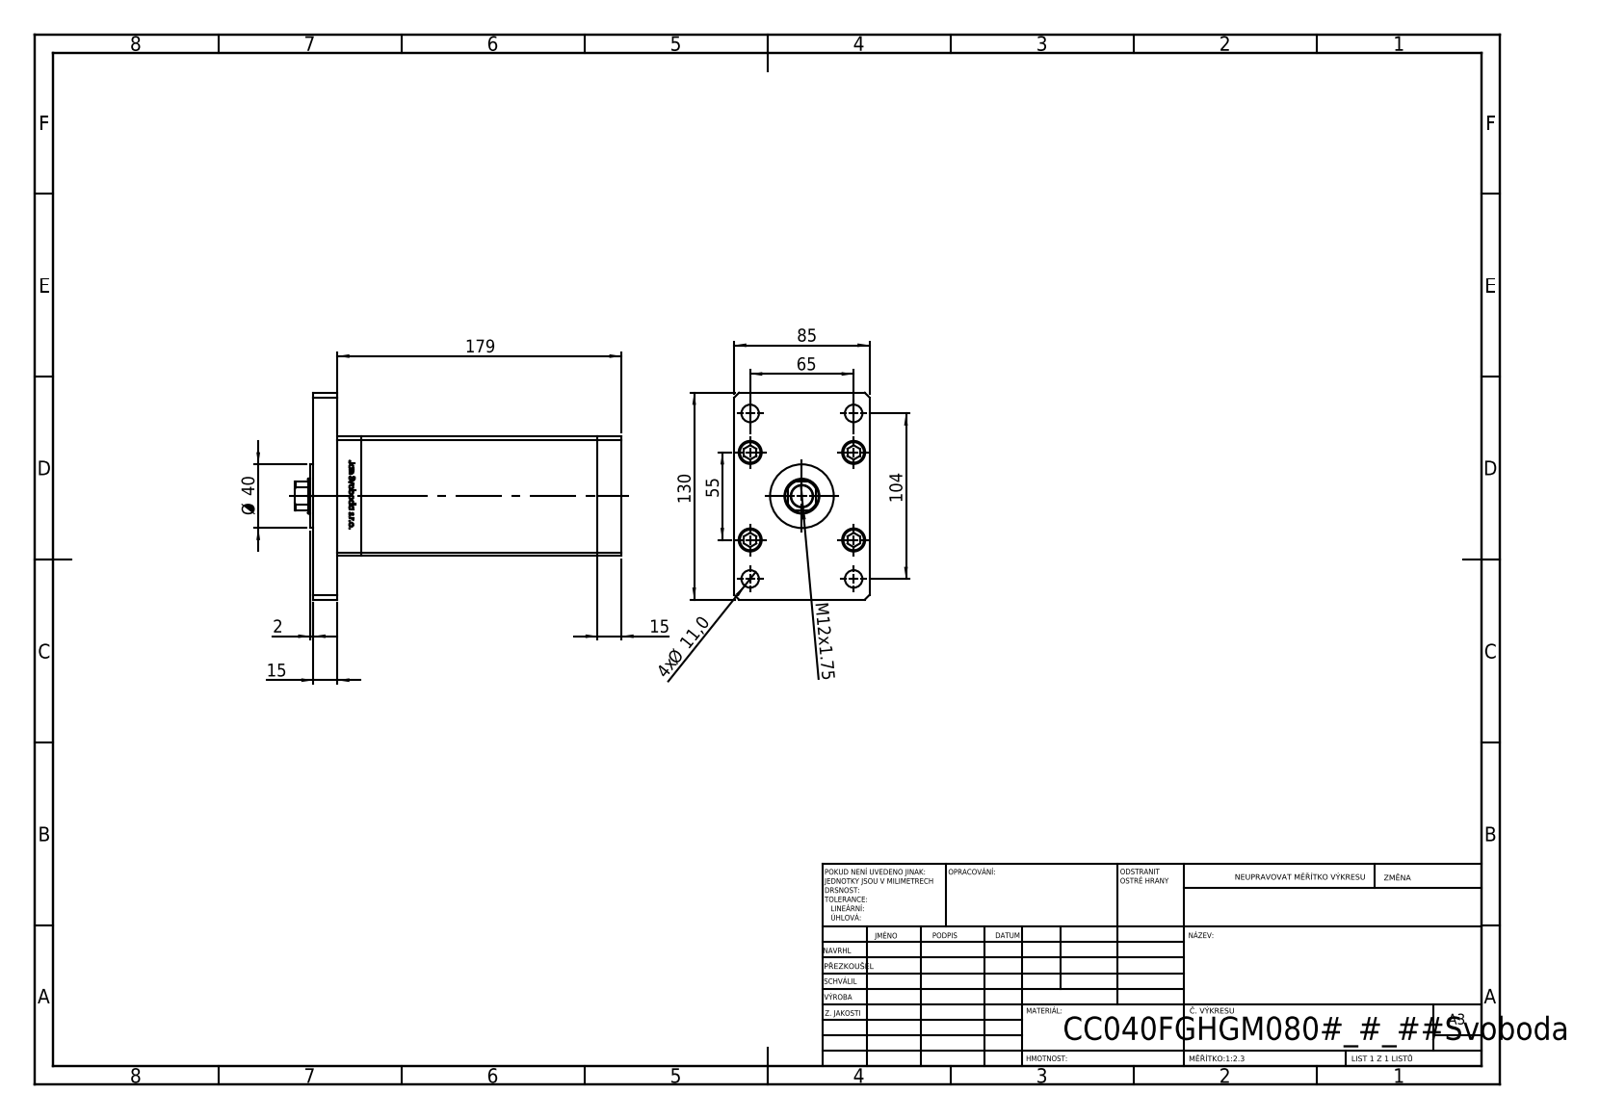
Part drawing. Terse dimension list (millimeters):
name: V220C_F_MIDDLE; V220C_F; V220C_FRONT_F; ALLEN BOLT (+2 more)
written by: SolidWorks 2019 (CONFIG_CONTROL_DESIGN)
unit: mm
bodies: 19 solids, 1308 faces (515 planar, 187 cylindrical, 606 other)
size: 205 × 130 × 85
volume: 1 165 000 mm³; area: 198 848 mm²
holes: 9× ⌀11, 5× ⌀15.5, 4× ⌀10, 4× ⌀14.5, 2× ⌀2, 2× ⌀13.16, 1× ⌀13.5, 1× ⌀22, 1× ⌀23.5
bosses: 9× ⌀8, 5× ⌀14.5, 1× ⌀40
rounds: 2× R0.93, 1× R10.5
face distances: 15, 85, 163.5, 178.5, 75, 148.5, 30, 193.5, 10.5, 27.5
hole spacings: 28, 24.5, 42.57, 61.32, 65, 69.46, 79.5, 102.69
